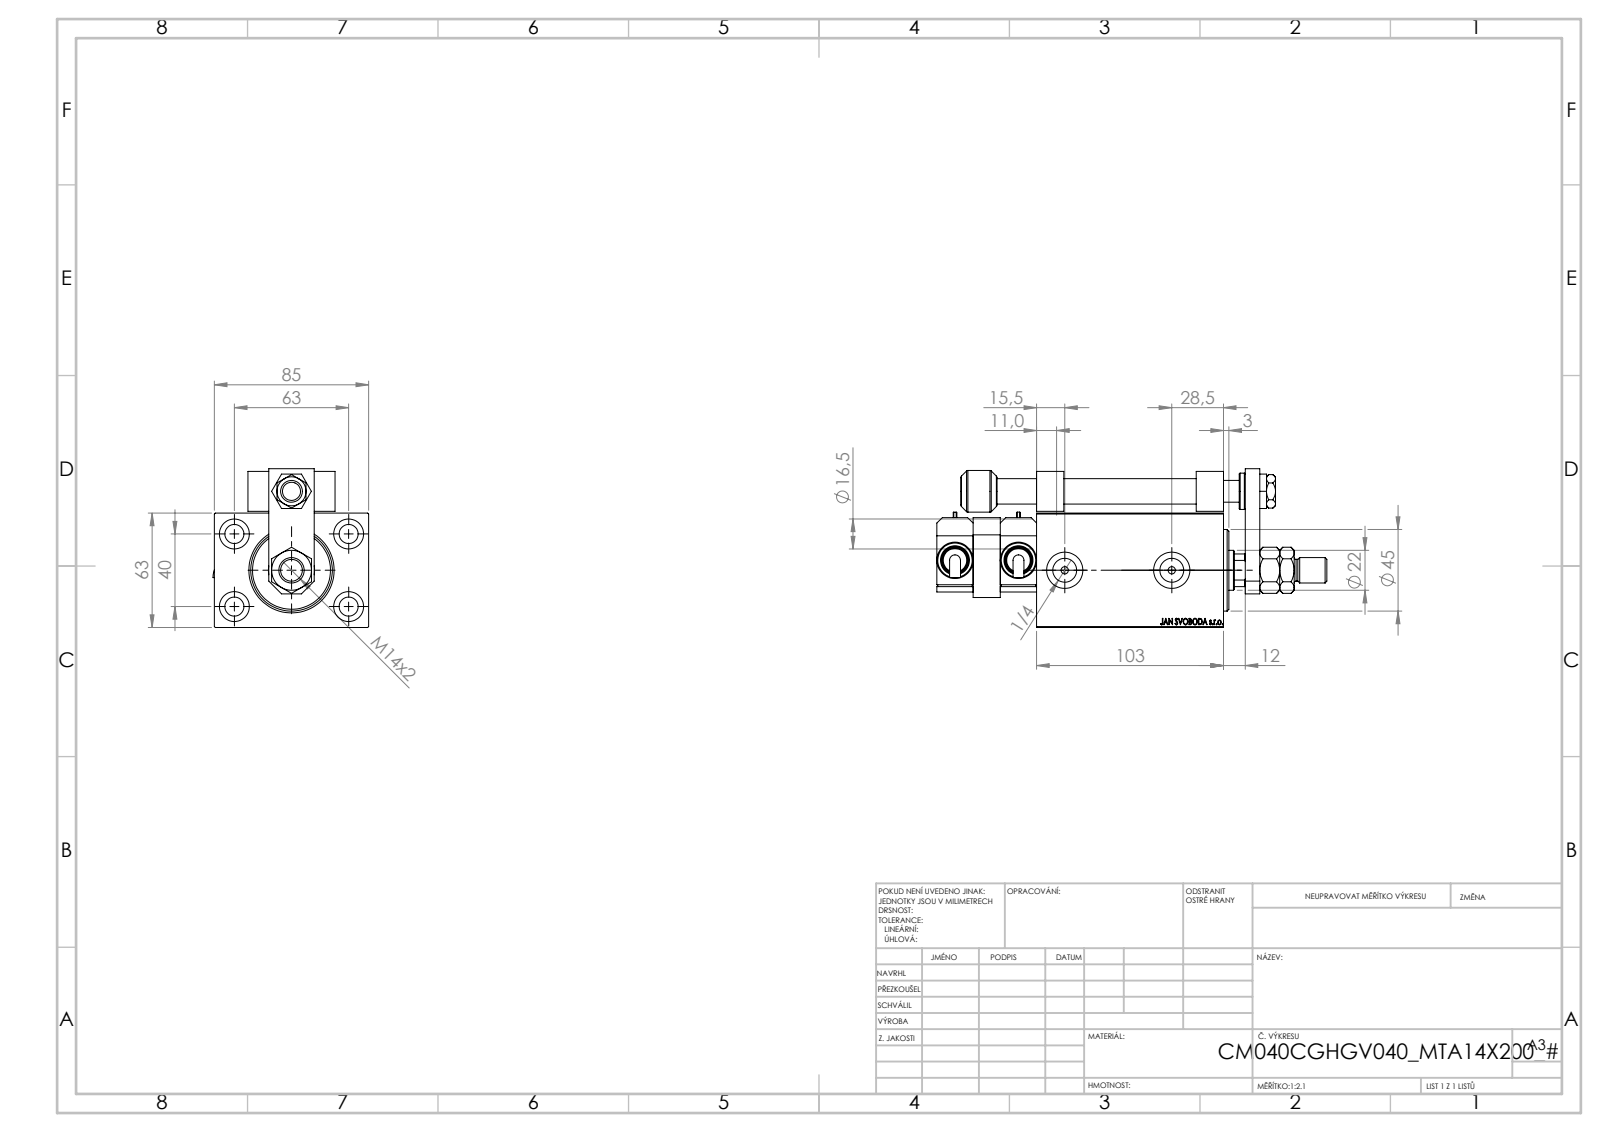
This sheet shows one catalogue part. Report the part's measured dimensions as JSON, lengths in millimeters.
{"part_name": "ZARAZKA_P; MIDDLE; SWITCH DIM W_B; P_V_Z_MTA (+7 more)", "step_written_by": "SolidWorks 2019 (CONFIG_CONTROL_DESIGN)", "units": "millimeters", "bodies": {"solids": 15, "faces": 1136, "planar": 535, "cylindrical": 122, "other": 479}, "overall_size": [215, 87.5, 85.76], "volume_mm3": 638587, "surface_area_mm2": 136304, "round_holes": [[4, 6], [16.5, 5], [8, 4], [10.5, 4], [13.16, 2], [20, 2], [12, 1], [12.5, 1], [13, 1], [14, 1], [22, 1], [25.5, 1]], "round_bosses_or_shafts": [[20, 3], [14, 3], [16, 2], [6, 2], [23, 1], [12, 1]], "partial_cylinders_radius": [[3, 1], [10.5, 1]], "face_to_face_distances": [63, 35, 20, 15, 123, 85, 12, 103, 91, 32], "hole_center_spacings": [37.31, 20, 39.3, 40, 63, 70.88, 74.63, 88]}
